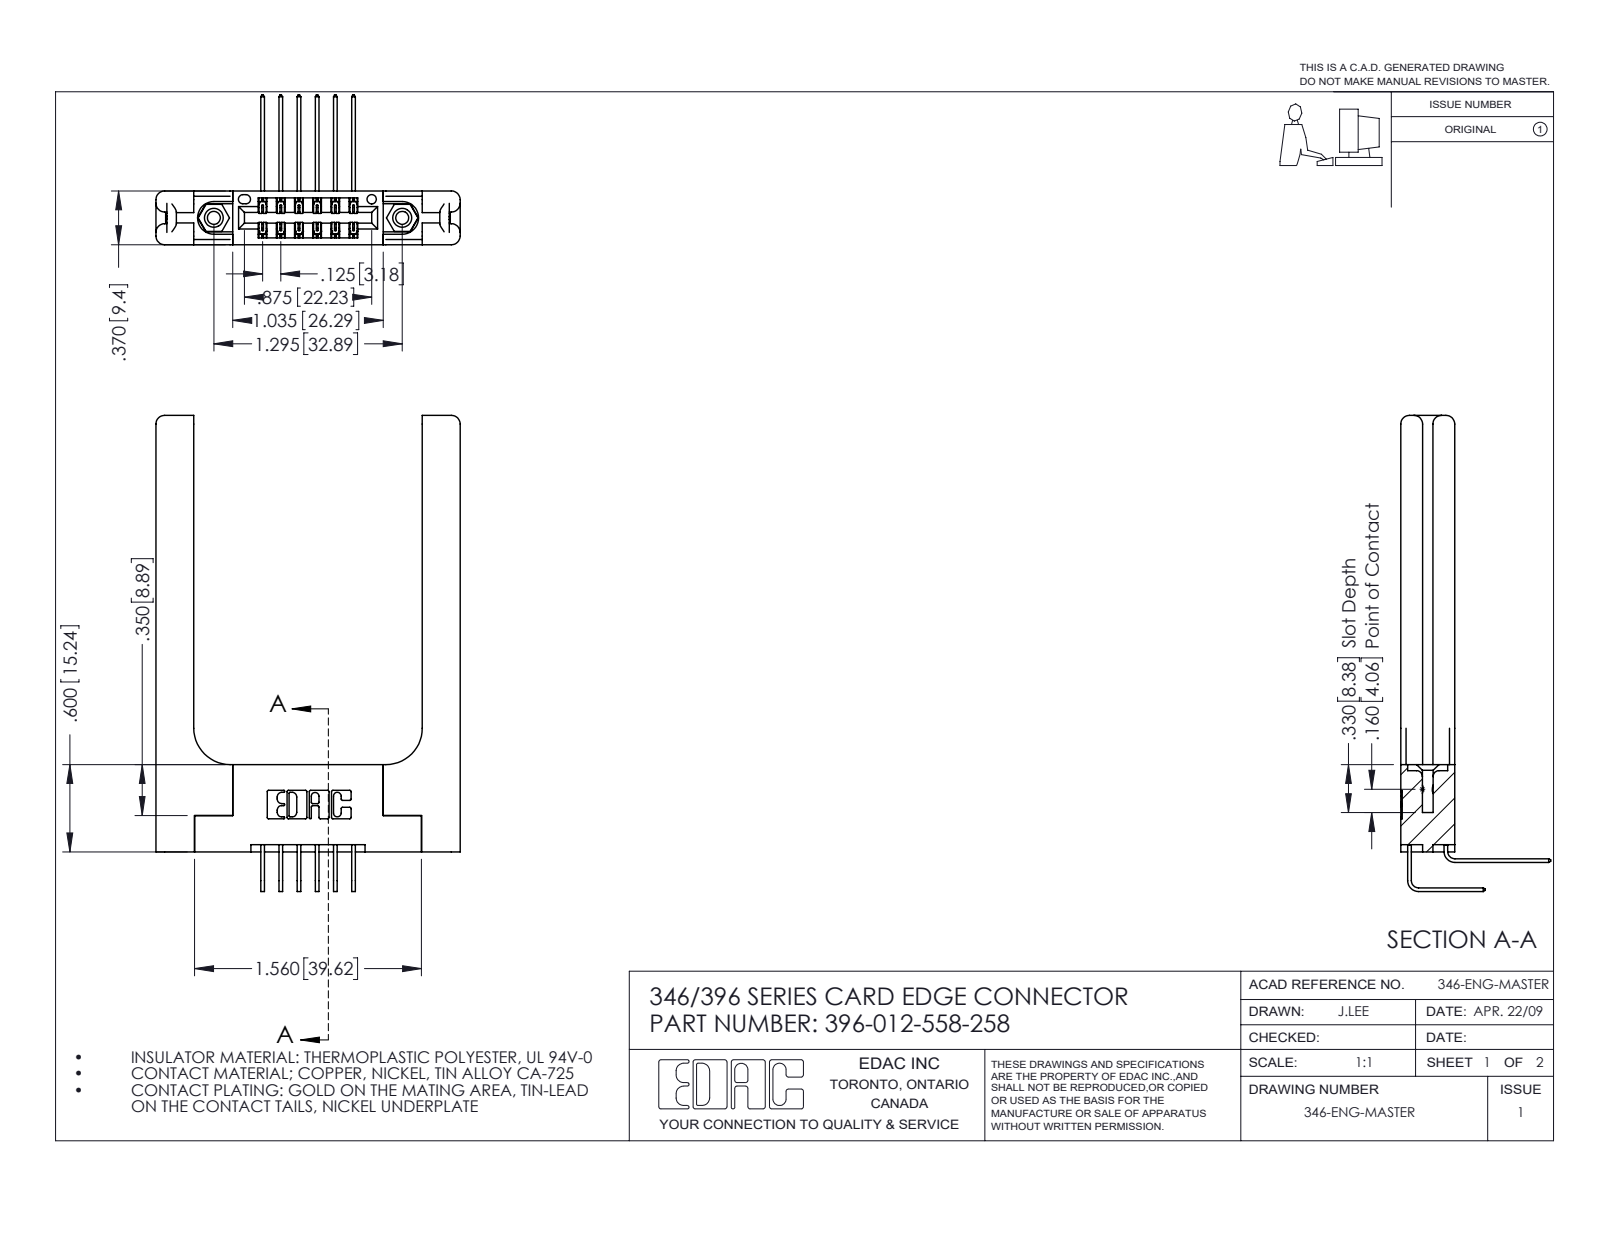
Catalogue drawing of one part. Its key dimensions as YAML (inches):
part_name: "345-250-001_345-250-001-102; 346 Part_Flush Mounting Lugs - 0.156 Dia-TH; 345-292-001_558 Tail - 2; 345-292-001_558 559 Tail - 1 (+2 more)"
step_written_by: "SolidWorks 2016 (CONFIG_CONTROL_DESIGN)"
units: inches
bodies: {solids: 17, faces: 1026, planar: 668, cylindrical: 298, other: 60}
overall_size: [3.273, 2.091, 1.03]
volume: 0.761
surface_area: 17.93
round_holes:
  - {diameter: 0.089, count: 2}
  - {diameter: 0.125, count: 2}
  - {diameter: 0.156, count: 2}
  - {diameter: 0.064, count: 1}
round_bosses_or_shafts:
  - {diameter: 0.155, count: 2}
partial_cylinders:
  - {radius: 0.01, count: 22}
  - {radius: 0.006, count: 18}
  - {radius: 0.06, count: 16}
  - {radius: 0.007, count: 6}
  - {radius: 0.031, count: 6}
  - {radius: 0.026, count: 3}
  - {radius: 0.014, count: 2}
  - {radius: 0.022, count: 2}
face_to_face_distances: [0.37, 0.15, 0.22, 0.072, 0.25, 0.322, 0.148, 0.048, 1.571, 0.025]
hole_center_spacings: [0.246, 1.092, 1.295]
